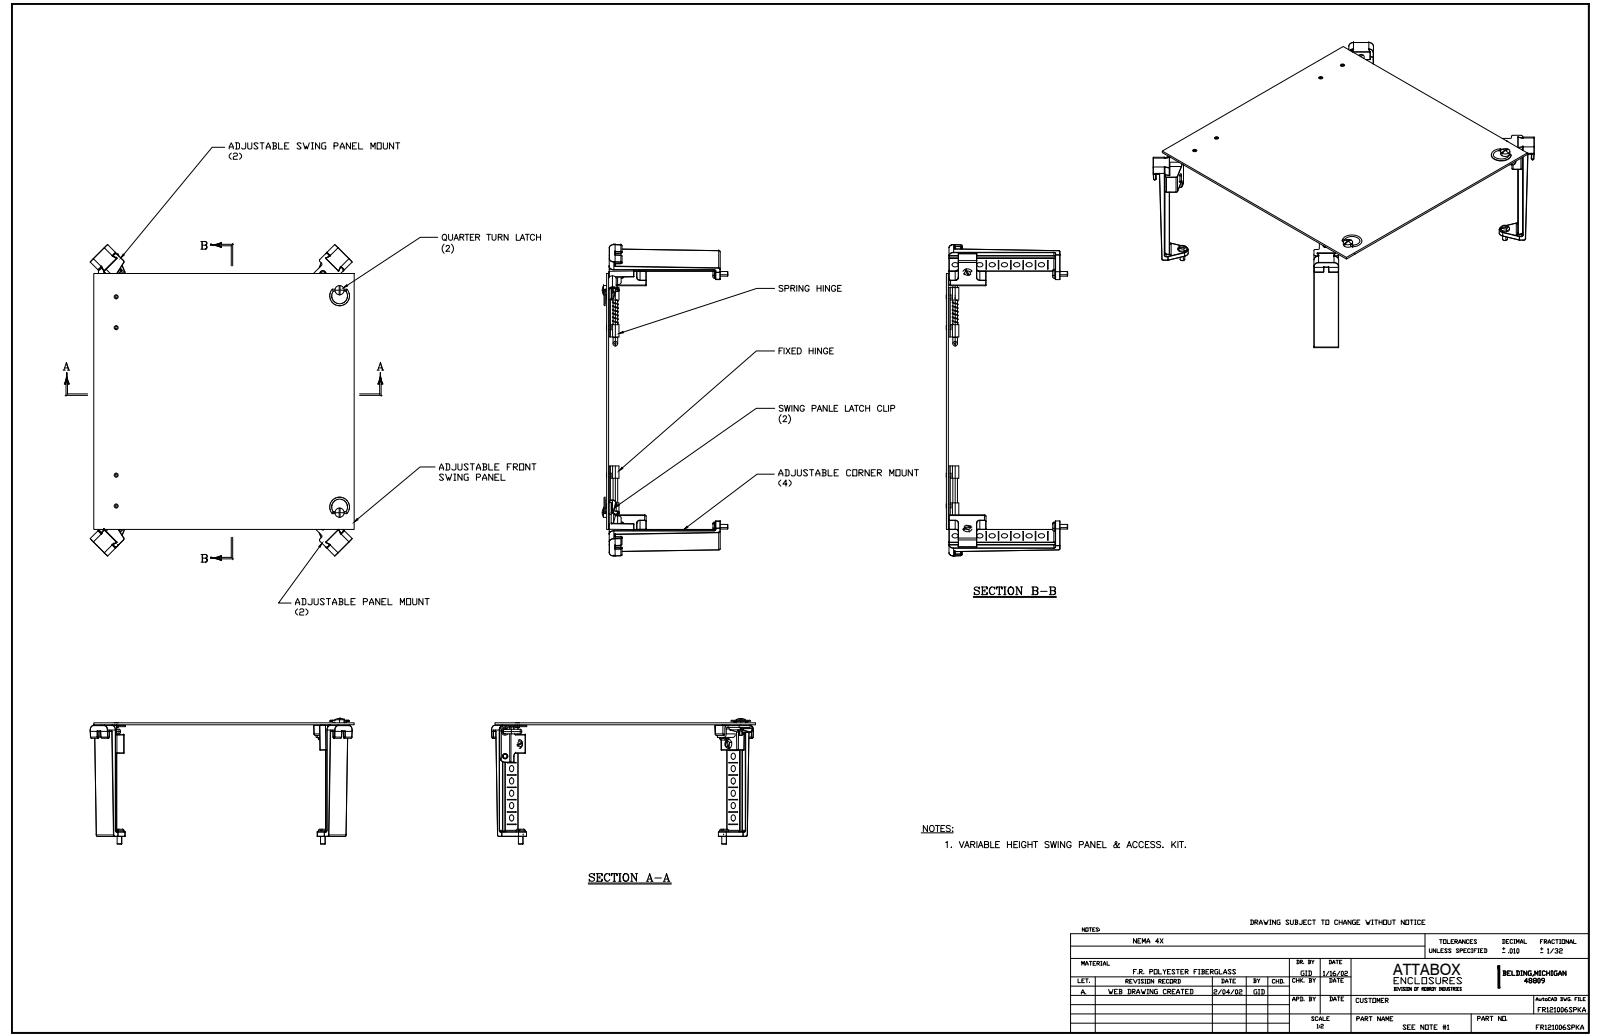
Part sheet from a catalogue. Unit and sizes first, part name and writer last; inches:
Units: inches
Overall size (bounding box): 12.622 × 10.622 × 4.703
Round holes (diameter × count): ⌀0.25 ×36, ⌀0.156 ×6, ⌀0.253 ×6, ⌀0.05 ×4, ⌀0.14 ×4, ⌀0.144 ×4, ⌀0.217 ×4, ⌀0.22 ×4, ⌀0.312 ×3, ⌀0.197 ×2, ⌀0.35 ×2, ⌀0.079 ×1
Round bosses / shafts (diameter × count): ⌀0.19 ×10, ⌀0.373 ×6, ⌀0.246 ×6, ⌀0.433 ×4, ⌀0.315 ×4, ⌀0.16 ×4, ⌀0.079 ×4, ⌀0.394 ×2
Partial cylindrical surfaces — rounded edges, fillets, slot ends (radius × count): R0.01 ×212, R0.06 ×44, R0.063 ×10, R0.025 ×8, R0.062 ×8, R0.13 ×6, R0.049 ×4, R0.19 ×4
Main face-to-face distances: 0.08, 14.124, 0.203, 14.326, 1, 7.057, 7.472, 6.855, 7.269, 6.057
Hole centre spacings: 1.5, 0.5, 1, 1.732, 2.061, 1.414, 2, 2.45
Volume: 17.69 in³ · Surface area: 354.3 in²
Bodies: 48 solids, 1801 faces (826 planar, 481 cylindrical, 494 other)
Part name (STEP PRODUCT): FR121006SPKA
STEP written by: SolidWorks 2019 (AUTOMOTIVE_DESIGN)
